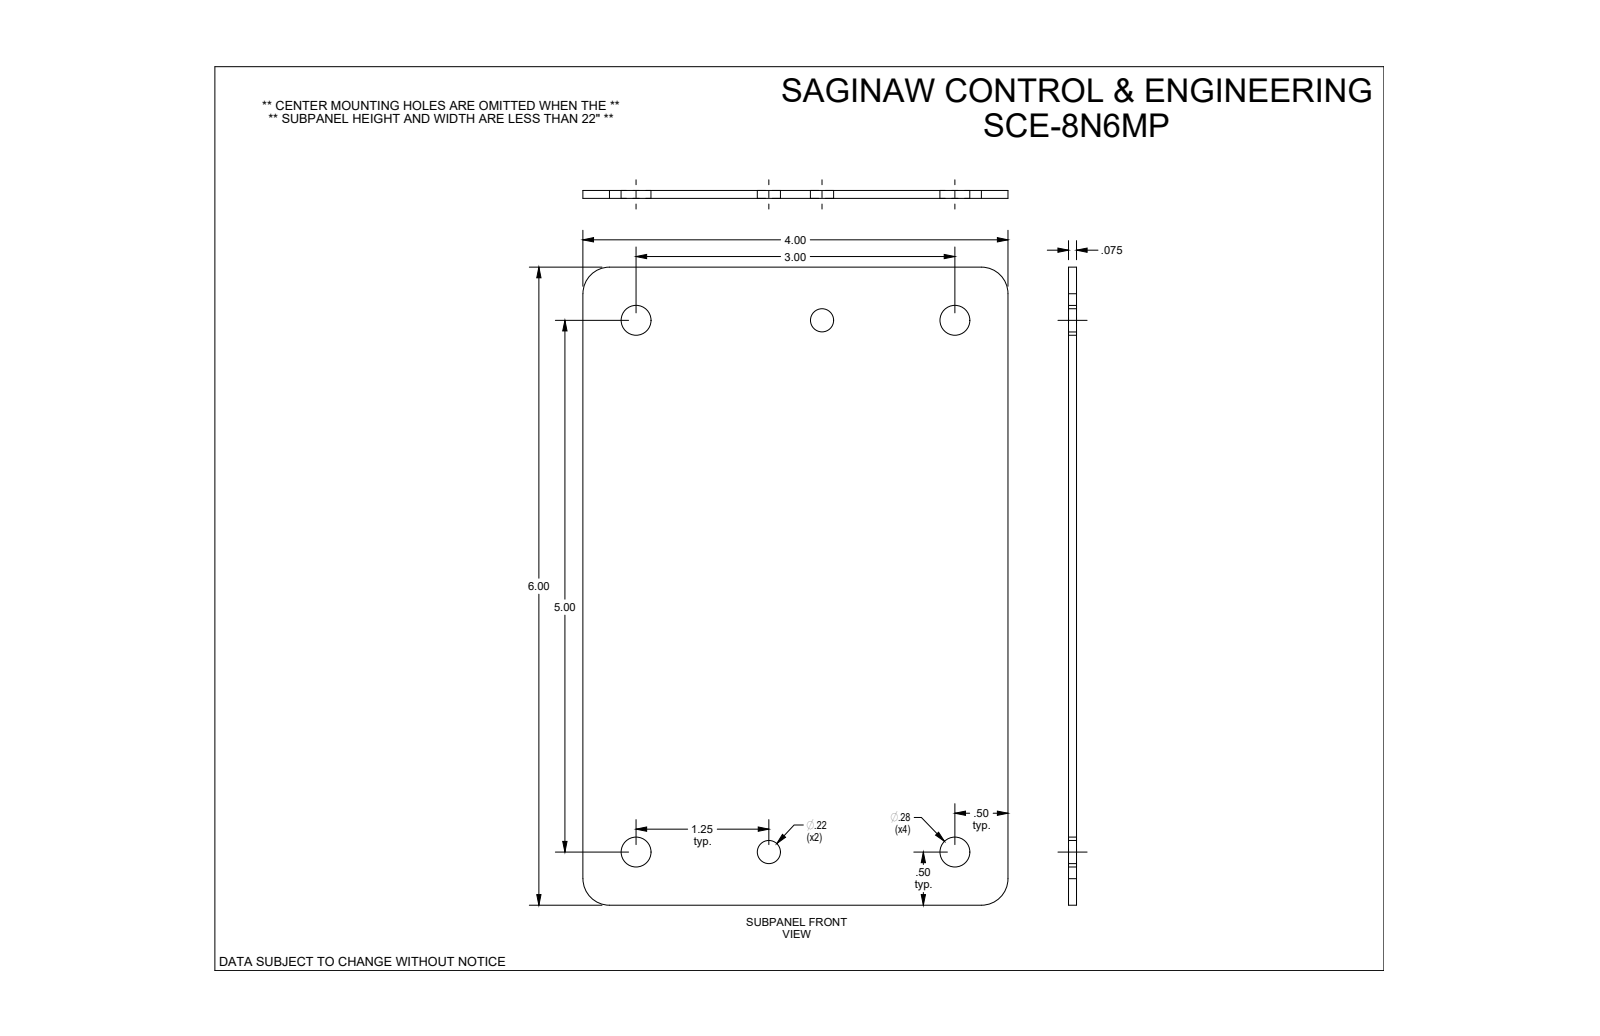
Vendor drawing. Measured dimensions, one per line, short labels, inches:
name: SCE-8N6MP
written by: SolidWorks 2019 (CONFIG_CONTROL_DESIGN)
unit: in
bodies: 1 solid, 16 faces (6 planar, 10 cylindrical, 0 other)
size: 6 × 4 × 0.075
volume: 1.772 in³; area: 49.08 in²
holes: 4× ⌀0.281, 2× ⌀0.218
rounds: 4× R0.25
face distances: 0.075, 4, 6
hole spacings: 1.25, 1.75, 3, 5, 5.154, 5.297, 5.831, 5.025
